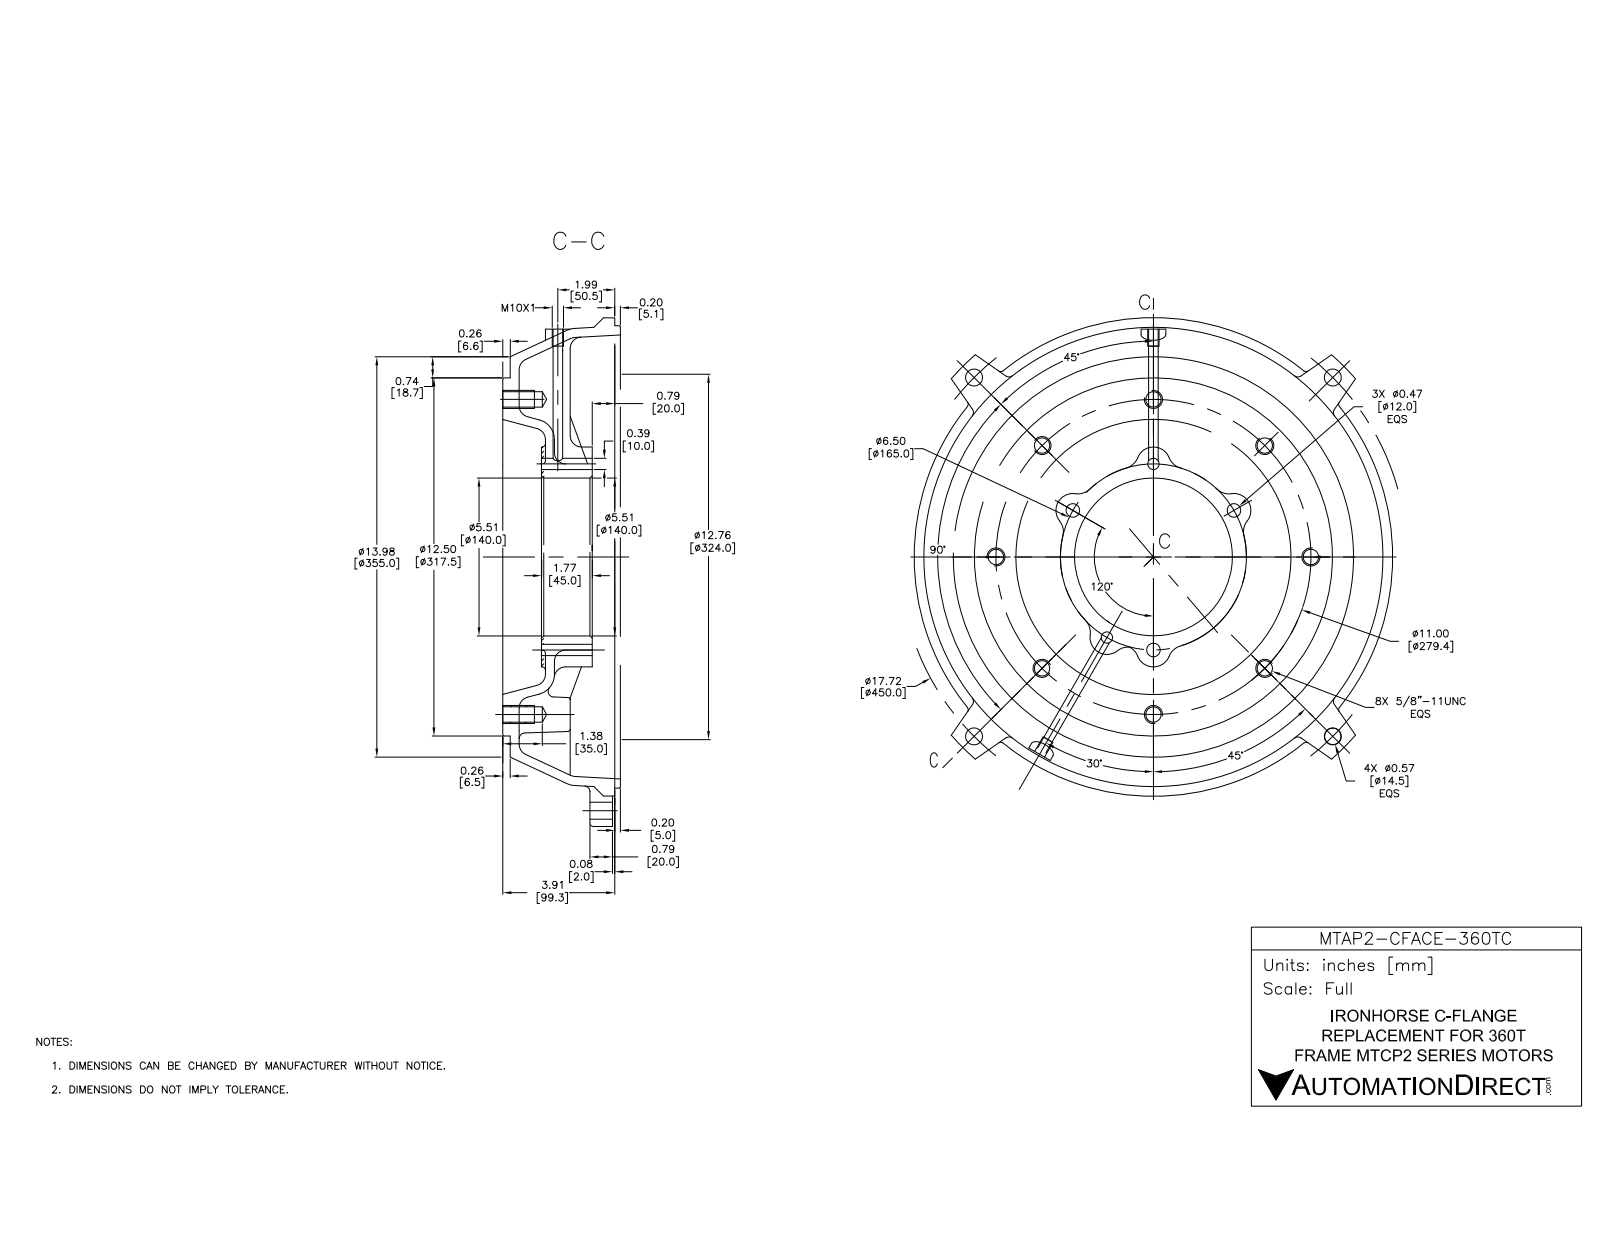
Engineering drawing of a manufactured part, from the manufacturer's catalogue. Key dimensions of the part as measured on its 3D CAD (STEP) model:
Part name (STEP PRODUCT): MTAP2-CFACE-360TC
STEP written by: SolidWorks 2017 (AUTOMOTIVE_DESIGN)
Units: inches
Bodies: 2 solids, 192 faces (42 planar, 109 cylindrical, 41 other)
Overall size (bounding box): 16.693 × 16.693 × 4.106
Volume: 355.9 in³ · Surface area: 812.8 in²
Round holes (diameter × count): ⌀0.63 ×8, ⌀0.571 ×4, ⌀0.472 ×3, ⌀0.275 ×1, ⌀3.465 ×1, ⌀5.512 ×1
Round bosses / shafts (diameter × count): ⌀16.693 ×1, ⌀16.142 ×1, ⌀12.5 ×1, ⌀7.677 ×1, ⌀3.937 ×1
Partial cylindrical surfaces — rounded edges, fillets, slot ends (radius × count): R0.591 ×15, R0.433 ×1, R3.248 ×1, R3.346 ×1, R9.409 ×1
Main face-to-face distances: 2.354, 0.256, 2.098, 1.024, 1.331, 1.075, 0.866, 1.555, 3.122, 2.866
Hole centre spacings: 5.5, 6.31, 13.328, 4.209, 7.778, 10.163, 10.427, 8.858
